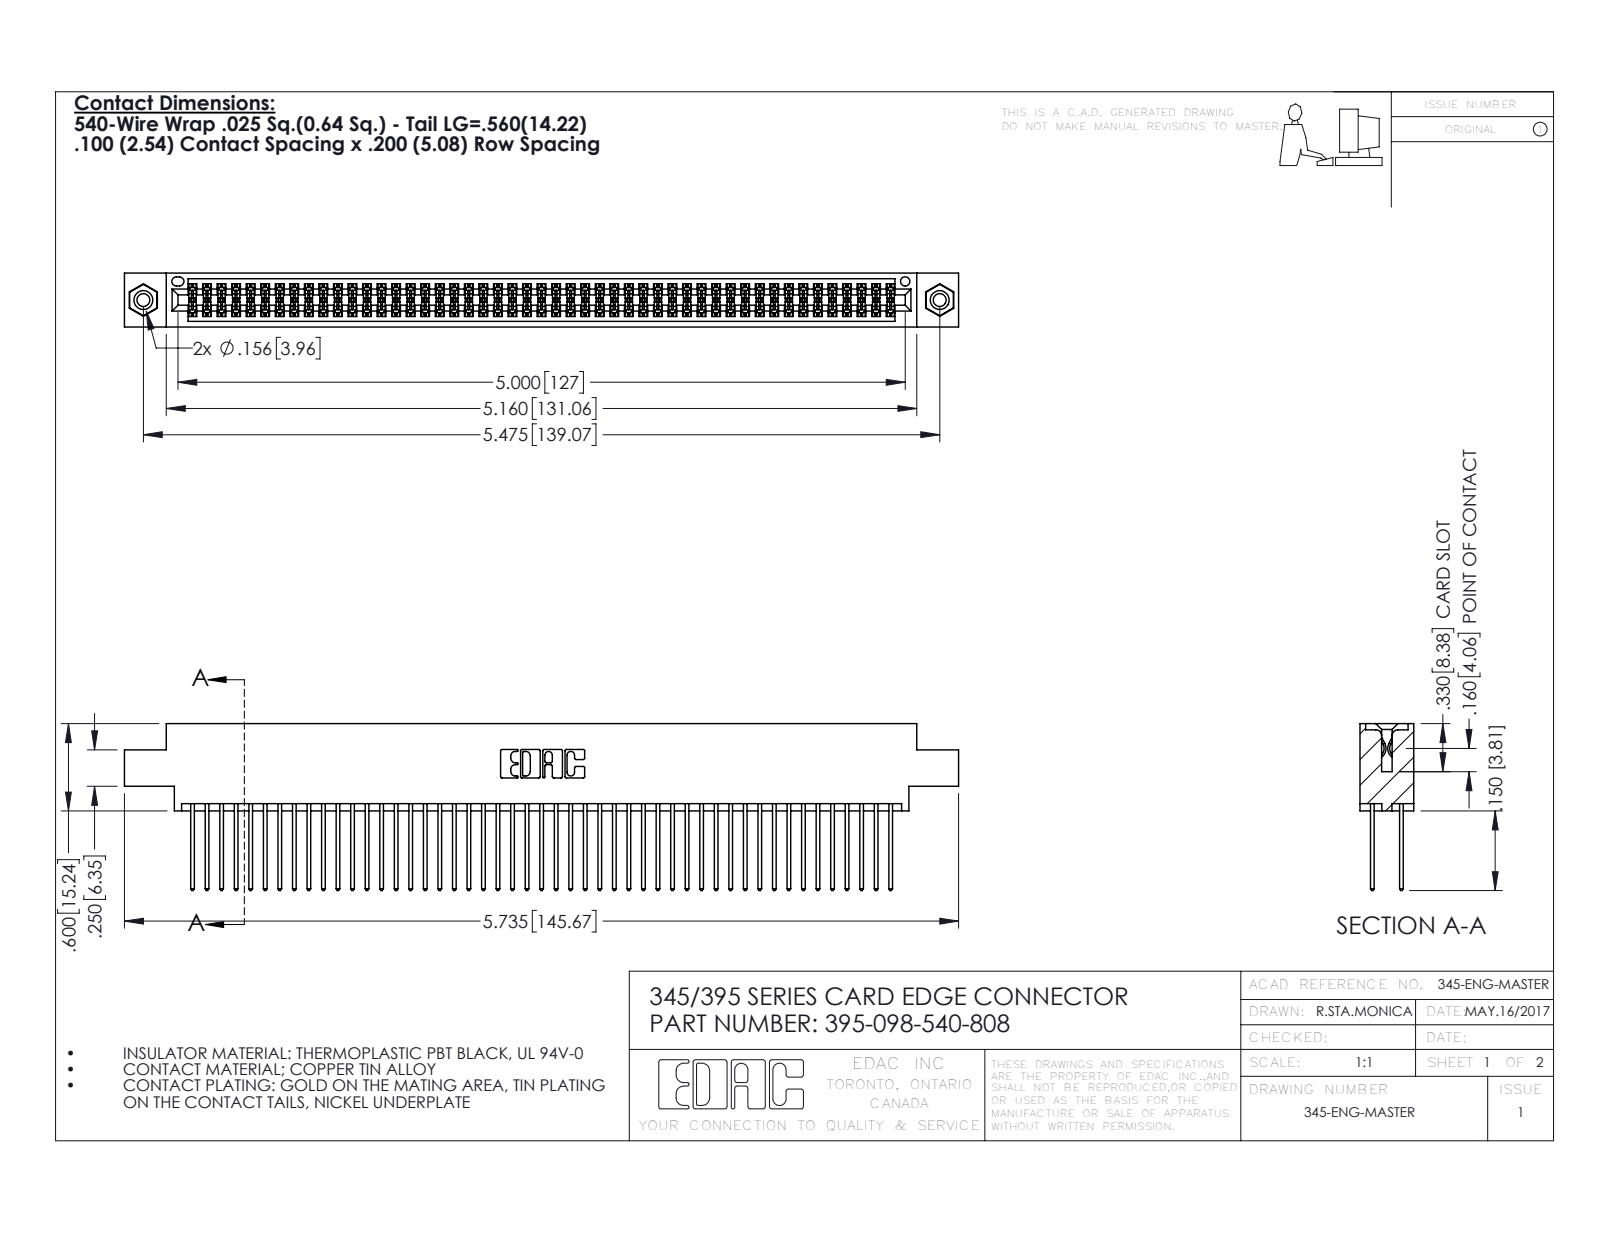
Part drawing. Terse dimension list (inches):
name: 345-292-001_345-293-140; 345-250-001_345-250-003-102; 345 Part_0.170 Offset - 0.156 Dia-TI; 395-098-540-808
written by: SolidWorks 2016 (CONFIG_CONTROL_DESIGN)
unit: in
bodies: 101 solids, 5090 faces (3350 planar, 1724 cylindrical, 16 other)
size: 5.735 × 1.147 × 0.37
volume: 0.883 in³; area: 36.27 in²
holes: 2× ⌀0.089, 2× ⌀0.125, 2× ⌀0.156, 1× ⌀0.064
bosses: 2× ⌀0.155
rounds: 147× R0.006, 98× R0.01, 22× R0.01, 6× R0.007, 6× R0.031, 3× R0.026, 2× R0.014, 2× R0.019
face distances: 0.072, 0.298, 0.2, 0.098, 0.272, 0.025, 0.37, 0.225, 0.175, 0.149
hole spacings: 0.27, 5.239, 5.475
